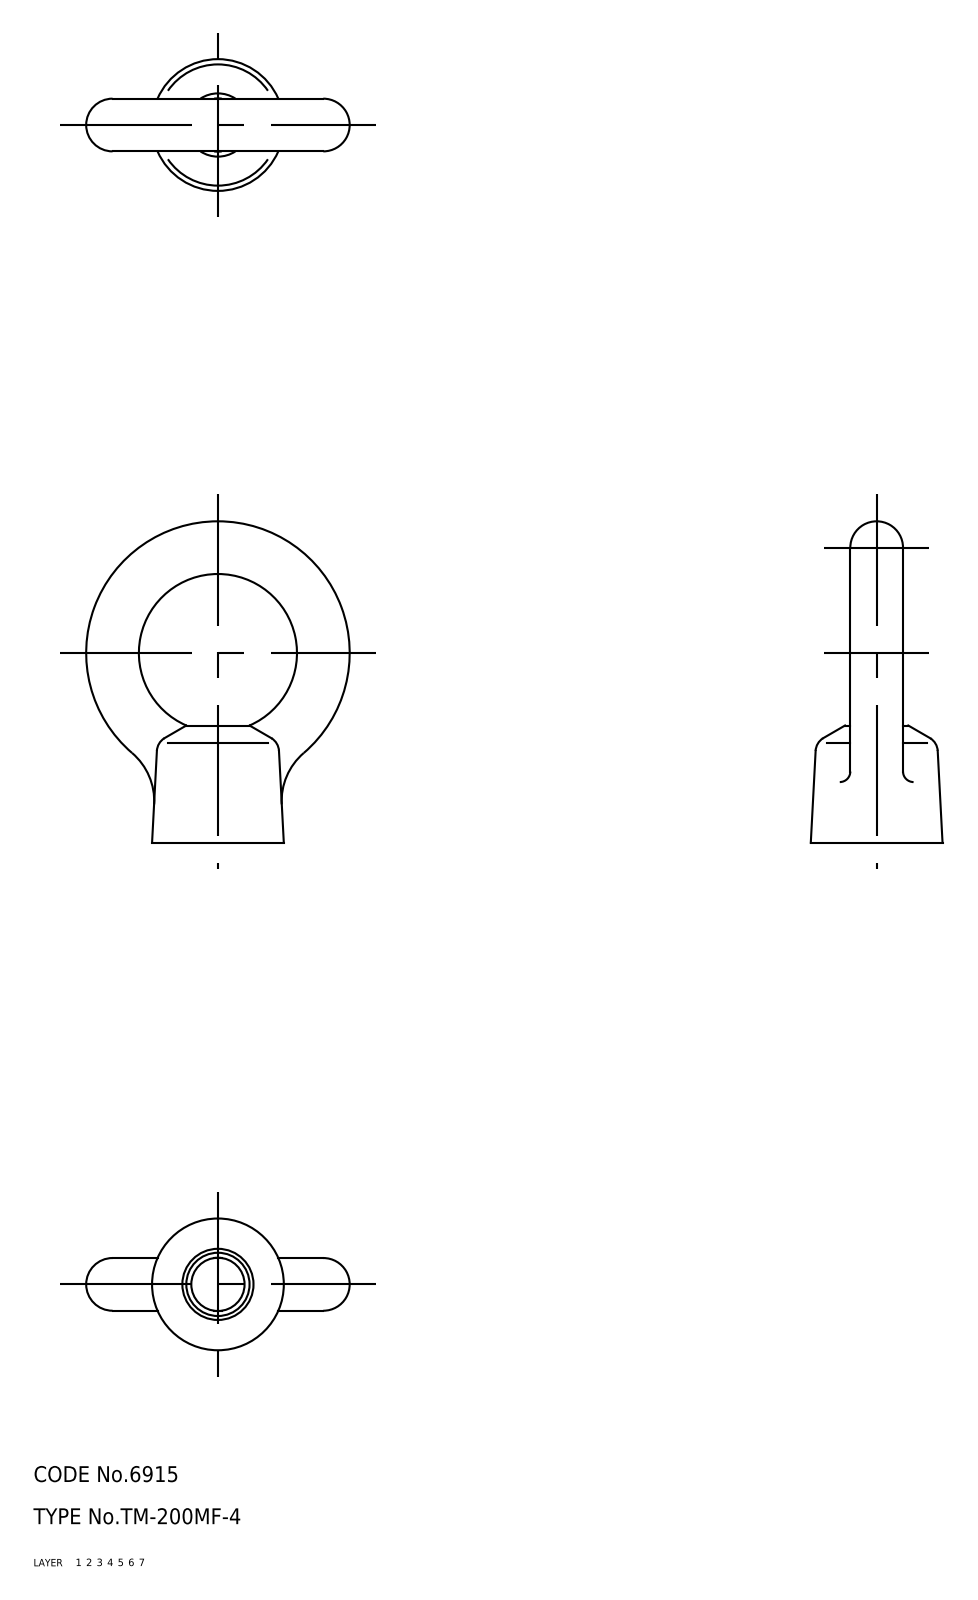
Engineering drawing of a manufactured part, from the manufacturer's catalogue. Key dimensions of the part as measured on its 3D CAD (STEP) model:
Part name (STEP PRODUCT): TM_200MF_4
STEP written by: SolidWorks 2003240 (AUTOMOTIVE_DESIGN)
Units: millimetres
Bodies: 1 solid, 19 faces (1 planar, 2 cylindrical, 16 other)
Overall size (bounding box): 61 × 50 × 25
Volume: 15 342 mm³ · Surface area: 6 130 mm²
Round holes (diameter × count): ⌀12 ×1
